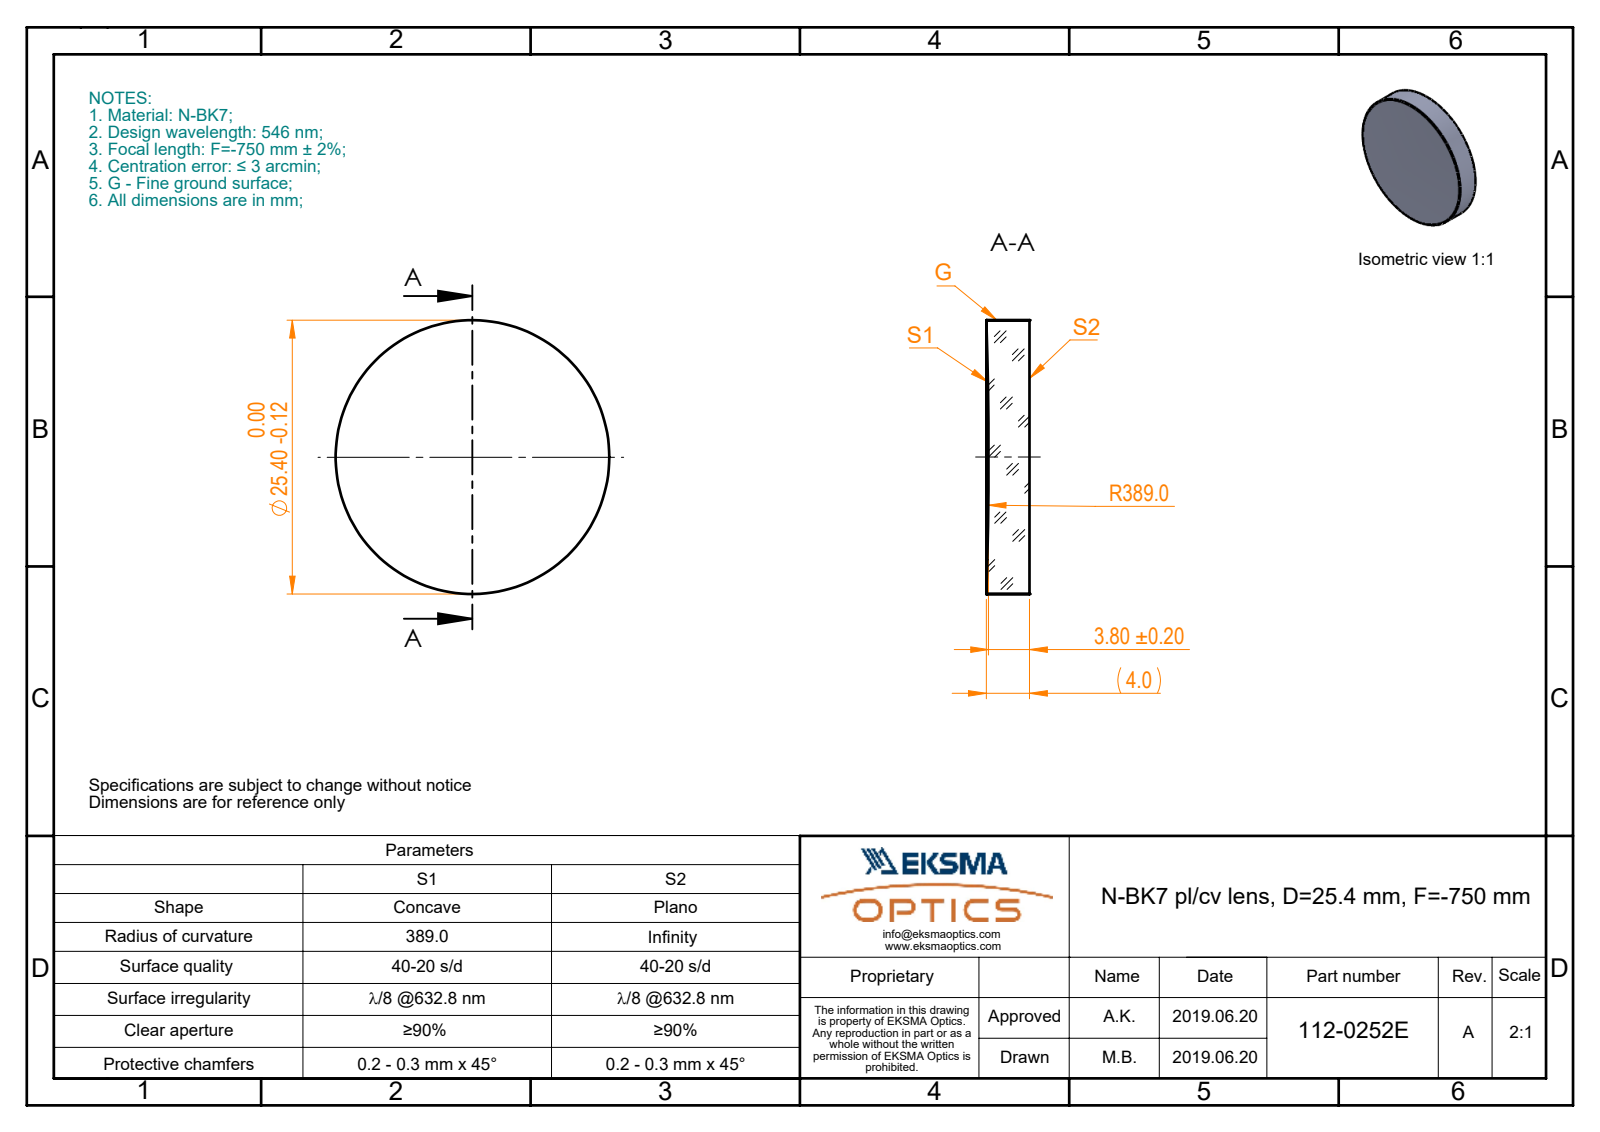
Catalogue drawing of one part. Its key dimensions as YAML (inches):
part_name: "112-0252E BK7 pl-cv 25.4 F-750"
step_written_by: "SolidWorks 2017 (CONFIG_CONTROL_DESIGN)"
units: inches
bodies: {solids: 1, faces: 5, planar: 1, cylindrical: 2, other: 2}
overall_size: [1, 1, 0.158]
volume: 0.121
surface_area: 2.066
round_bosses_or_shafts:
  - {diameter: 1, count: 1}
